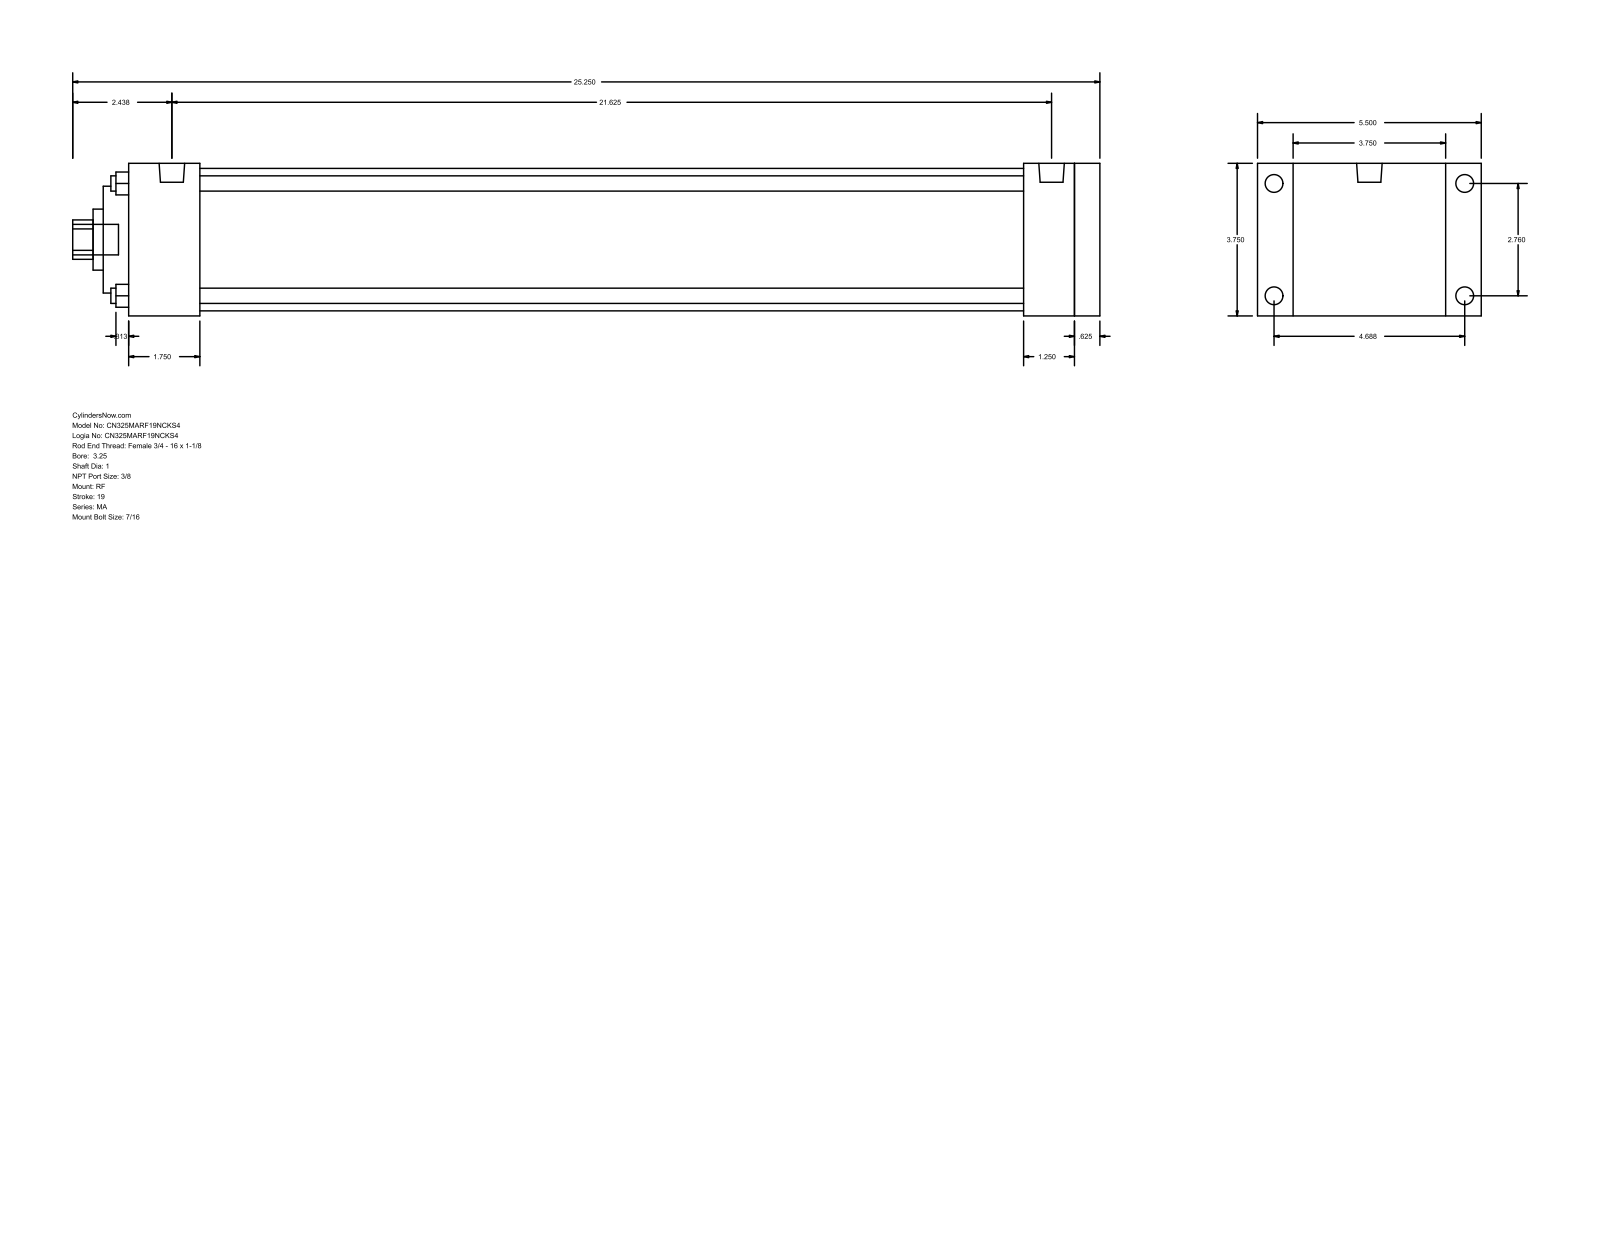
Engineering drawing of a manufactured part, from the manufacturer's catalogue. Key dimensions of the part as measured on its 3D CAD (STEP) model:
Part name (STEP PRODUCT): MA_RF__0325_1
STEP written by: GSSL Pune (CONFIG_CONTROL_DESIGN)
Units: millimetres
Bodies: 0 solids, 94 faces (65 planar, 29 cylindrical, 0 other)
Overall size (bounding box): 641.35 × 139.7 × 95.25
Round holes (diameter × count): ⌀9.53 ×4, ⌀25.4 ×1, ⌀38.1 ×1, ⌀66.67 ×1, ⌀88.9 ×1
Round bosses / shafts (diameter × count): ⌀11.11 ×8, ⌀15.93 ×2, ⌀19.05 ×1
Partial cylindrical surfaces — rounded edges, fillets, slot ends (radius × count): R12.29 ×1
Main face-to-face distances: 95.24, 606.43, 15.87, 590.56, 22.23, 117.47, 558.81, 31.75, 47.62, 44.46
Hole centre spacings: 49.57, 70.1, 99.14
